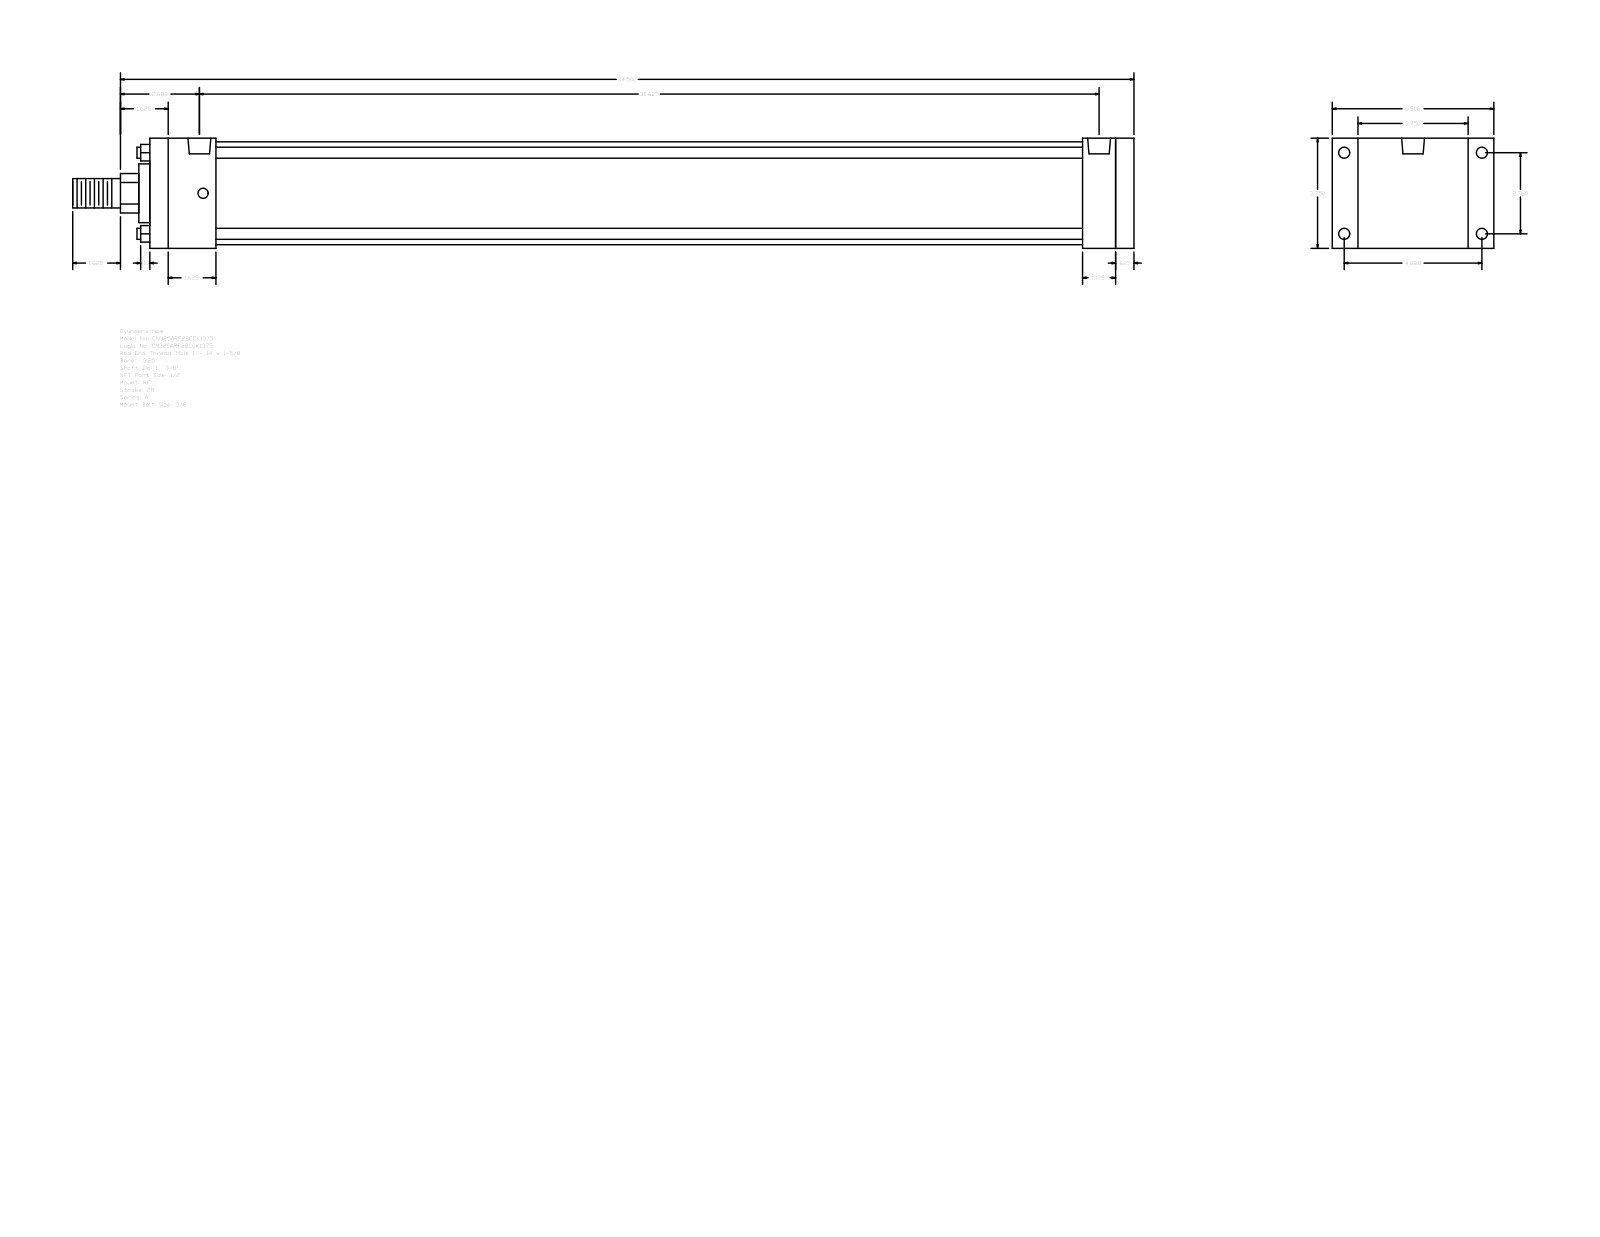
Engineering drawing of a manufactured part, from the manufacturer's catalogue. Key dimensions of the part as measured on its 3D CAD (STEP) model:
Part name (STEP PRODUCT): A_RF__0325_1.375
STEP written by: GSSL Pune (CONFIG_CONTROL_DESIGN)
Units: millimetres
Bodies: 0 solids, 92 faces (64 planar, 28 cylindrical, 0 other)
Overall size (bounding box): 917.58 × 139.7 × 95.25
Round holes (diameter × count): ⌀8.73 ×4, ⌀9.53 ×4, ⌀19.77 ×2
Round bosses / shafts (diameter × count): ⌀9.53 ×4, ⌀88.9 ×1, ⌀50.8 ×1, ⌀34.92 ×1, ⌀25.4 ×1
Partial cylindrical surfaces — rounded edges, fillets, slot ends (radius × count): R17.06 ×1
Main face-to-face distances: 95.24, 850.9, 15.88, 835.02, 57.15, 22.23, 117.47, 806.45, 28.57, 44.45
Hole centre spacings: 3.18, 70.1, 119.06, 138.16, 771.52, 774.7, 777.88
